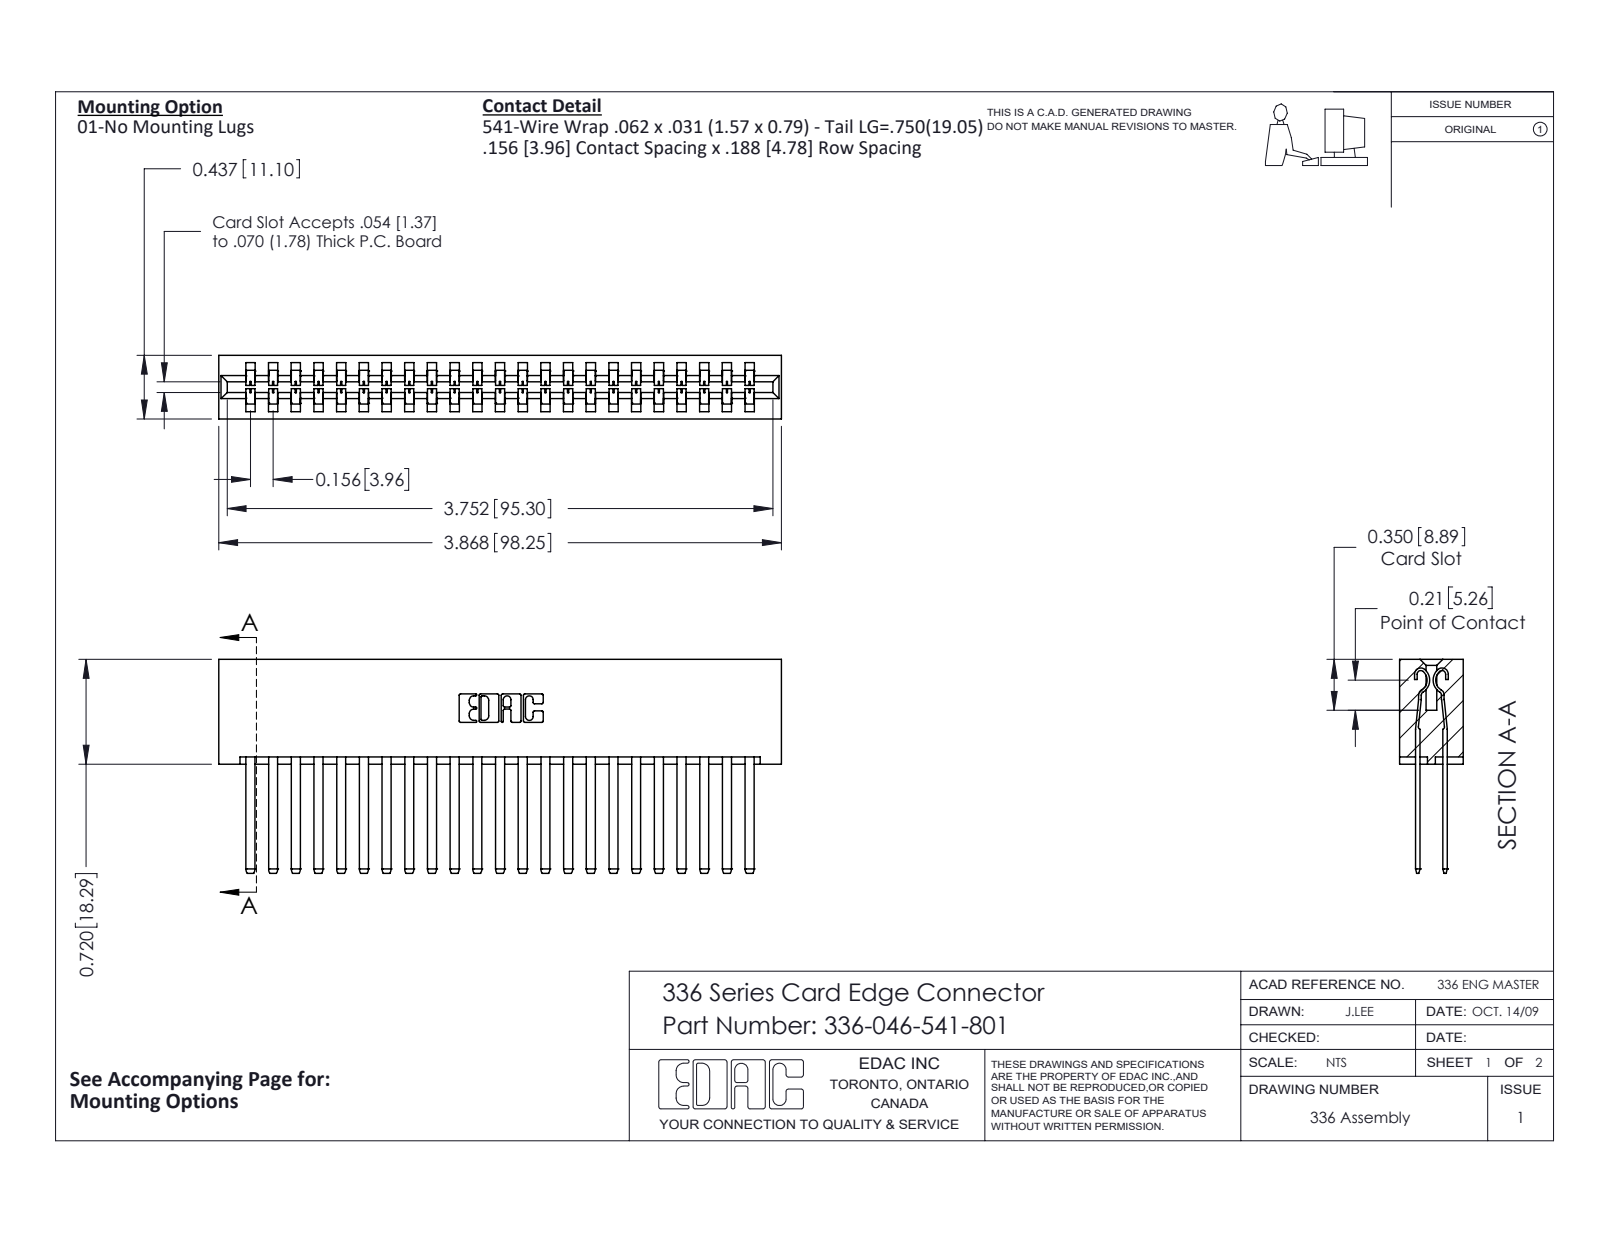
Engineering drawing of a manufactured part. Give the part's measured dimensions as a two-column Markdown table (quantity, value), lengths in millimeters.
| quantity | value |
| --- | --- |
| part name | 336 Part_Lugless; 336-046-541-801; 336-290-001_336-290-541 |
| STEP written by | SolidWorks 2020 (CONFIG_CONTROL_DESIGN) |
| units | millimeters |
| bodies | 47 solids, 2038 faces (1262 planar, 776 cylindrical, 0 other) |
| overall size | 98.2 × 37.3 × 11.1 |
| volume | 16 200 mm³ |
| surface area | 20 570 mm² |
| partial cylindrical surfaces (radius × count) | 0.1 × 92, 1.4 × 46, 0.3 × 22, 0.2 × 6, 0.8 × 6, 0.6 × 4, 1 × 4, 0.7 × 3 |
| main face-to-face distances | 4.8, 8.3, 3.6, 7.5, 2.8, 0.8, 11.1, 0.8, 4, 4.6 |
